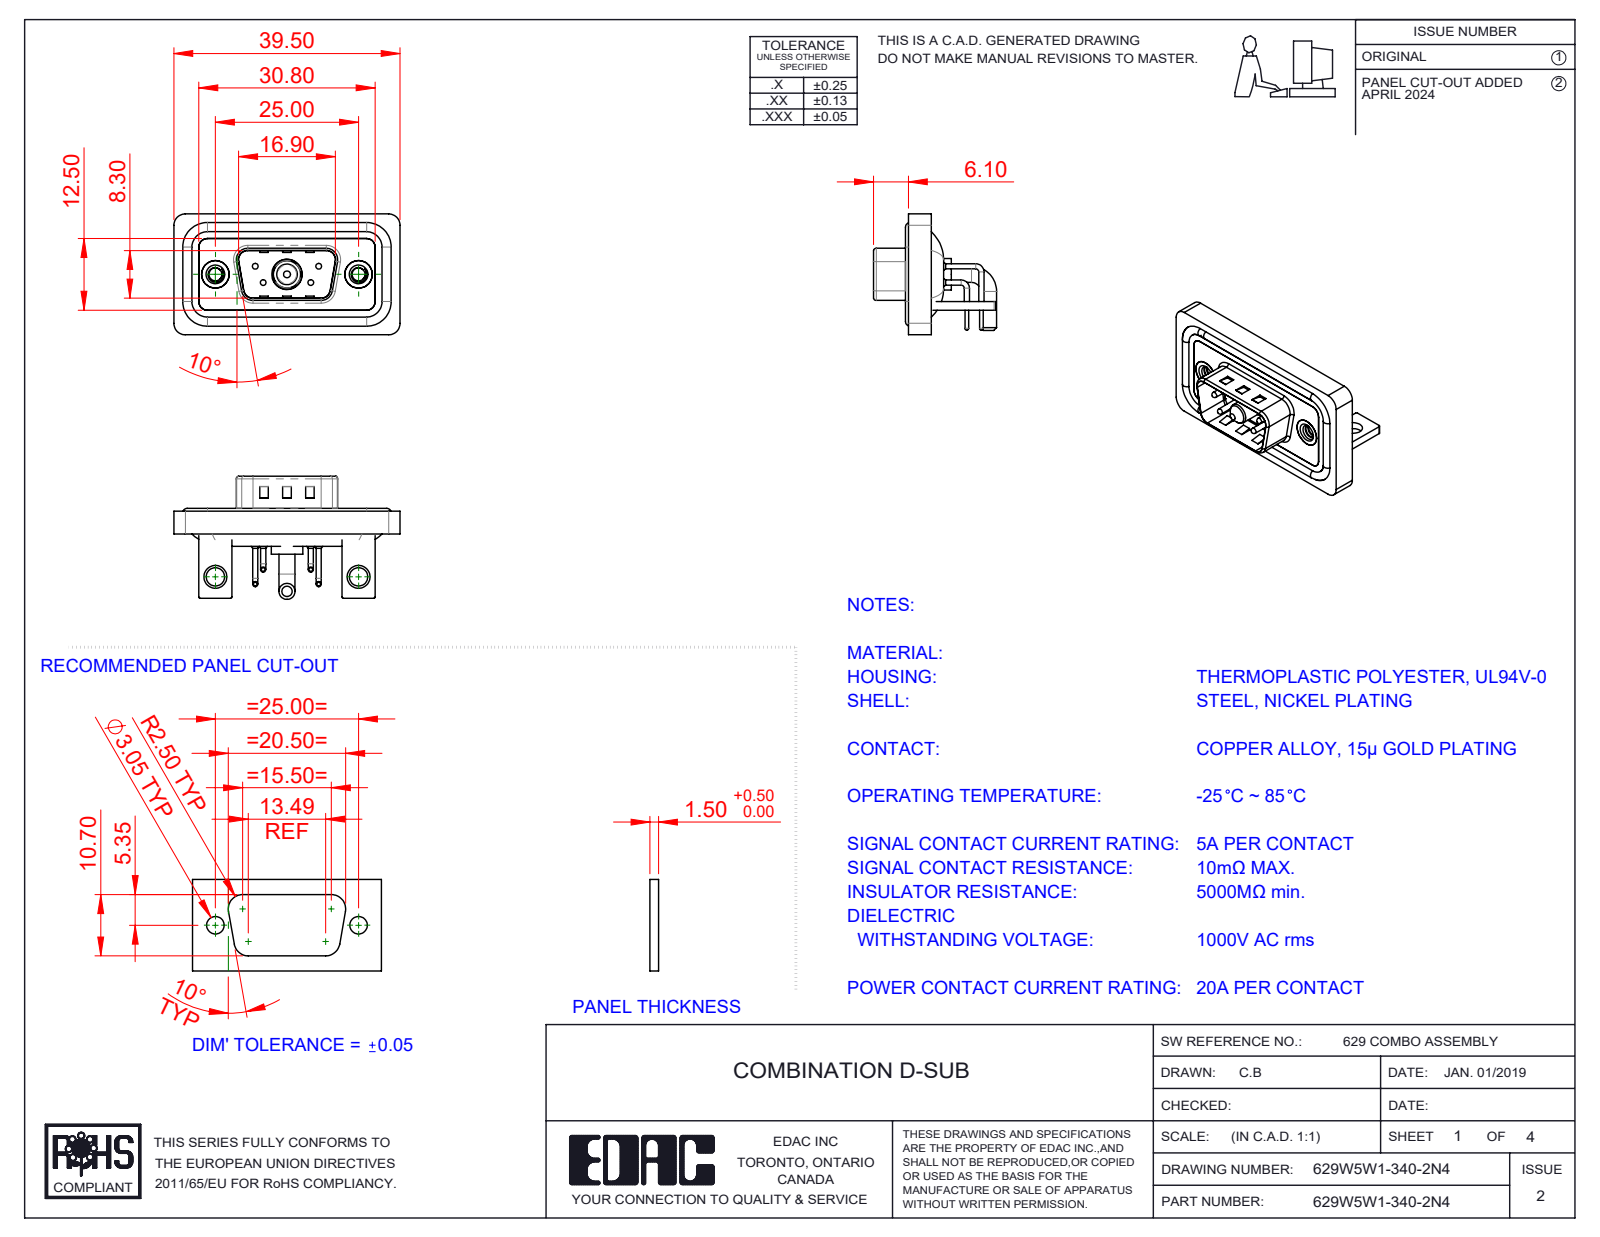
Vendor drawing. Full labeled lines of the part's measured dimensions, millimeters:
Part name (STEP PRODUCT): 629Combo Stabilizer Bracket; 629Combo Waterproof Housing_09 Contacts; 629Combo Contact Row 1; Power Pin_20A RA (+6 more)
STEP written by: SolidWorks 2023 (CONFIG_CONTROL_DESIGN)
Units: millimetres
Bodies: 15 solids, 934 faces (431 planar, 363 cylindrical, 140 other)
Overall size (bounding box): 39.5 × 21.5 × 21.1
Volume: 4 753 mm³ · Surface area: 7 750 mm²
Round holes (diameter × count): ⌀0.75 ×4, ⌀1.6 ×4, ⌀2 ×4, ⌀2.26 ×2, ⌀3.2 ×2, ⌀4 ×2, ⌀4.8 ×2, ⌀5 ×2, ⌀4.85 ×1, ⌀5.3 ×1
Round bosses / shafts (diameter × count): ⌀0.9 ×8, ⌀1.6 ×4, ⌀1.5 ×4, ⌀1 ×4, ⌀0.65 ×4, ⌀4.9 ×2, ⌀2.8 ×2, ⌀5.5 ×1
Partial cylindrical surfaces — rounded edges, fillets, slot ends (radius × count): R2 ×19, R1.5 ×18, R0.25 ×16, R0.5 ×9, R1.6 ×8, R0.6 ×4, R0.65 ×4, R0.9 ×4
Main face-to-face distances: 0.4, 1.5, 0.8, 2.9, 1.1, 2.1, 1.2, 1.6, 2.5, 3.7
Hole centre spacings: 3.16, 5.72, 7.1, 12.5, 18.1, 25, 4.39, 4.4
